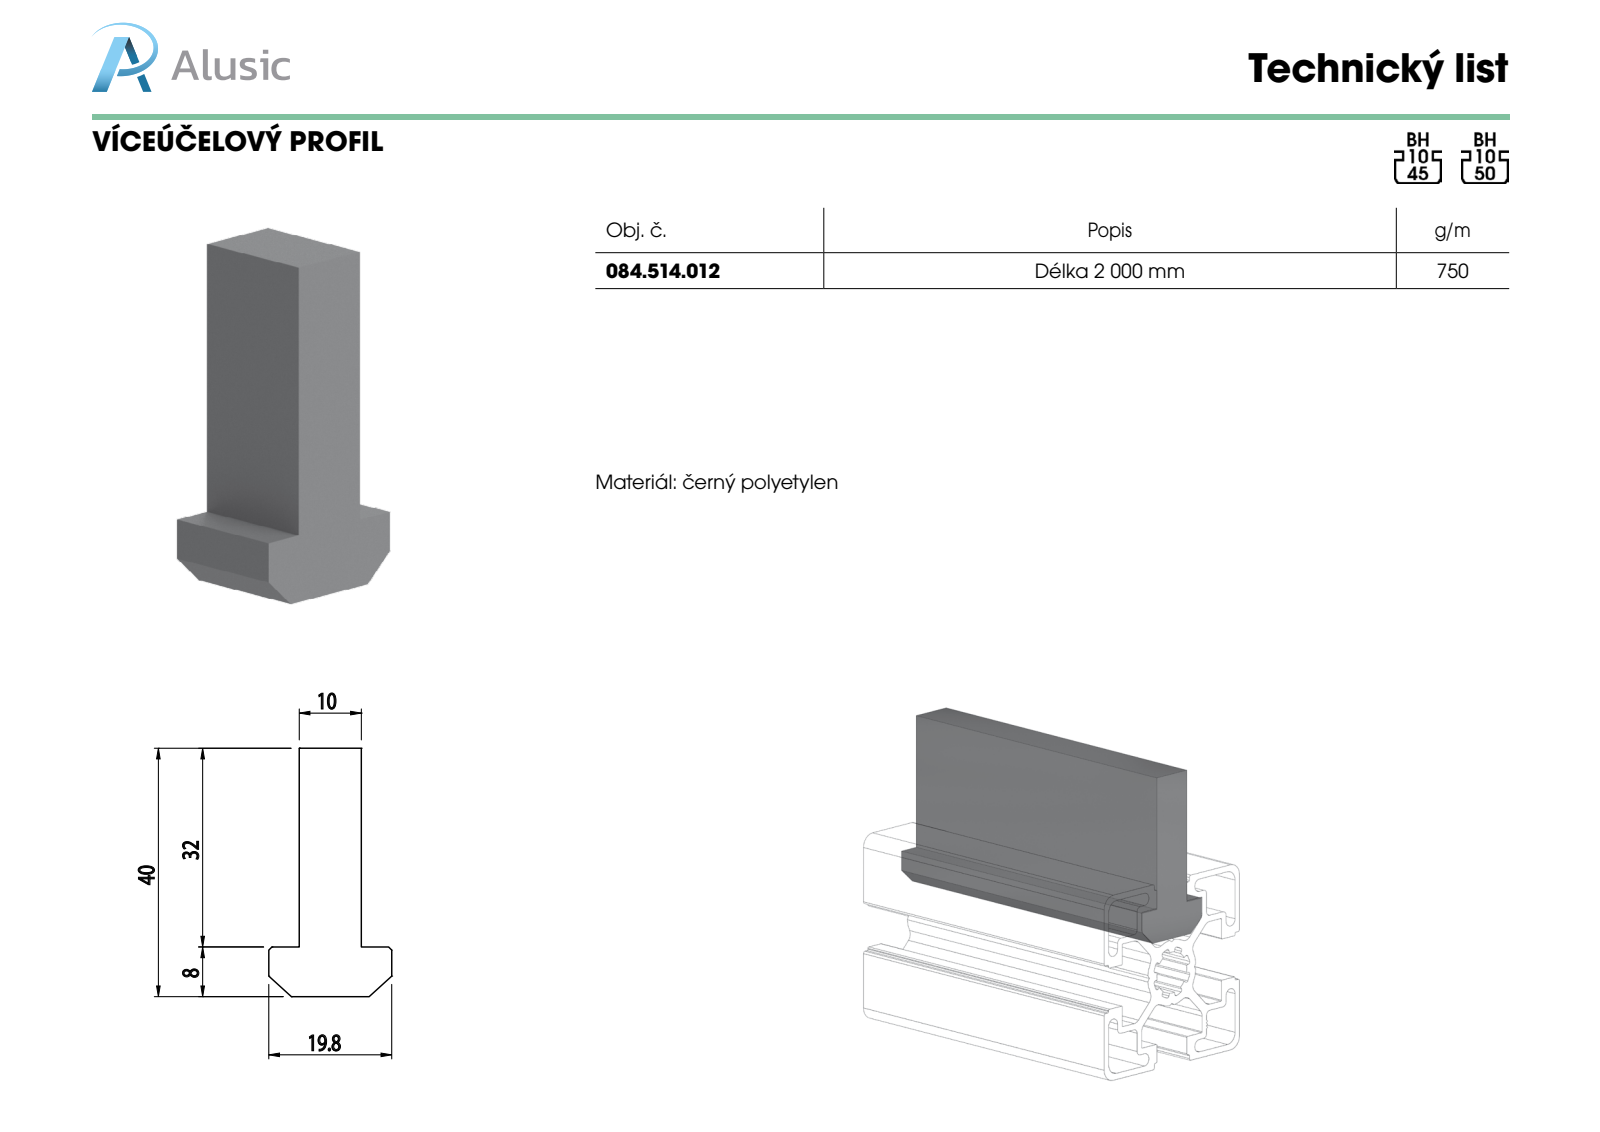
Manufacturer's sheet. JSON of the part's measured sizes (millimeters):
{"part_name": "084.514.012", "step_written_by": "SolidWorks 2011 (CONFIG_CONTROL_DESIGN)", "units": "millimeters", "bodies": {"solids": 1, "faces": 12, "planar": 12, "cylindrical": 0, "other": 0}, "overall_size": [100, 40, 19.8], "volume_mm3": 46634, "surface_area_mm2": 12487, "face_to_face_distances": [10, 40, 8, 32, 4.9, 14.9, 19.8, 100]}
